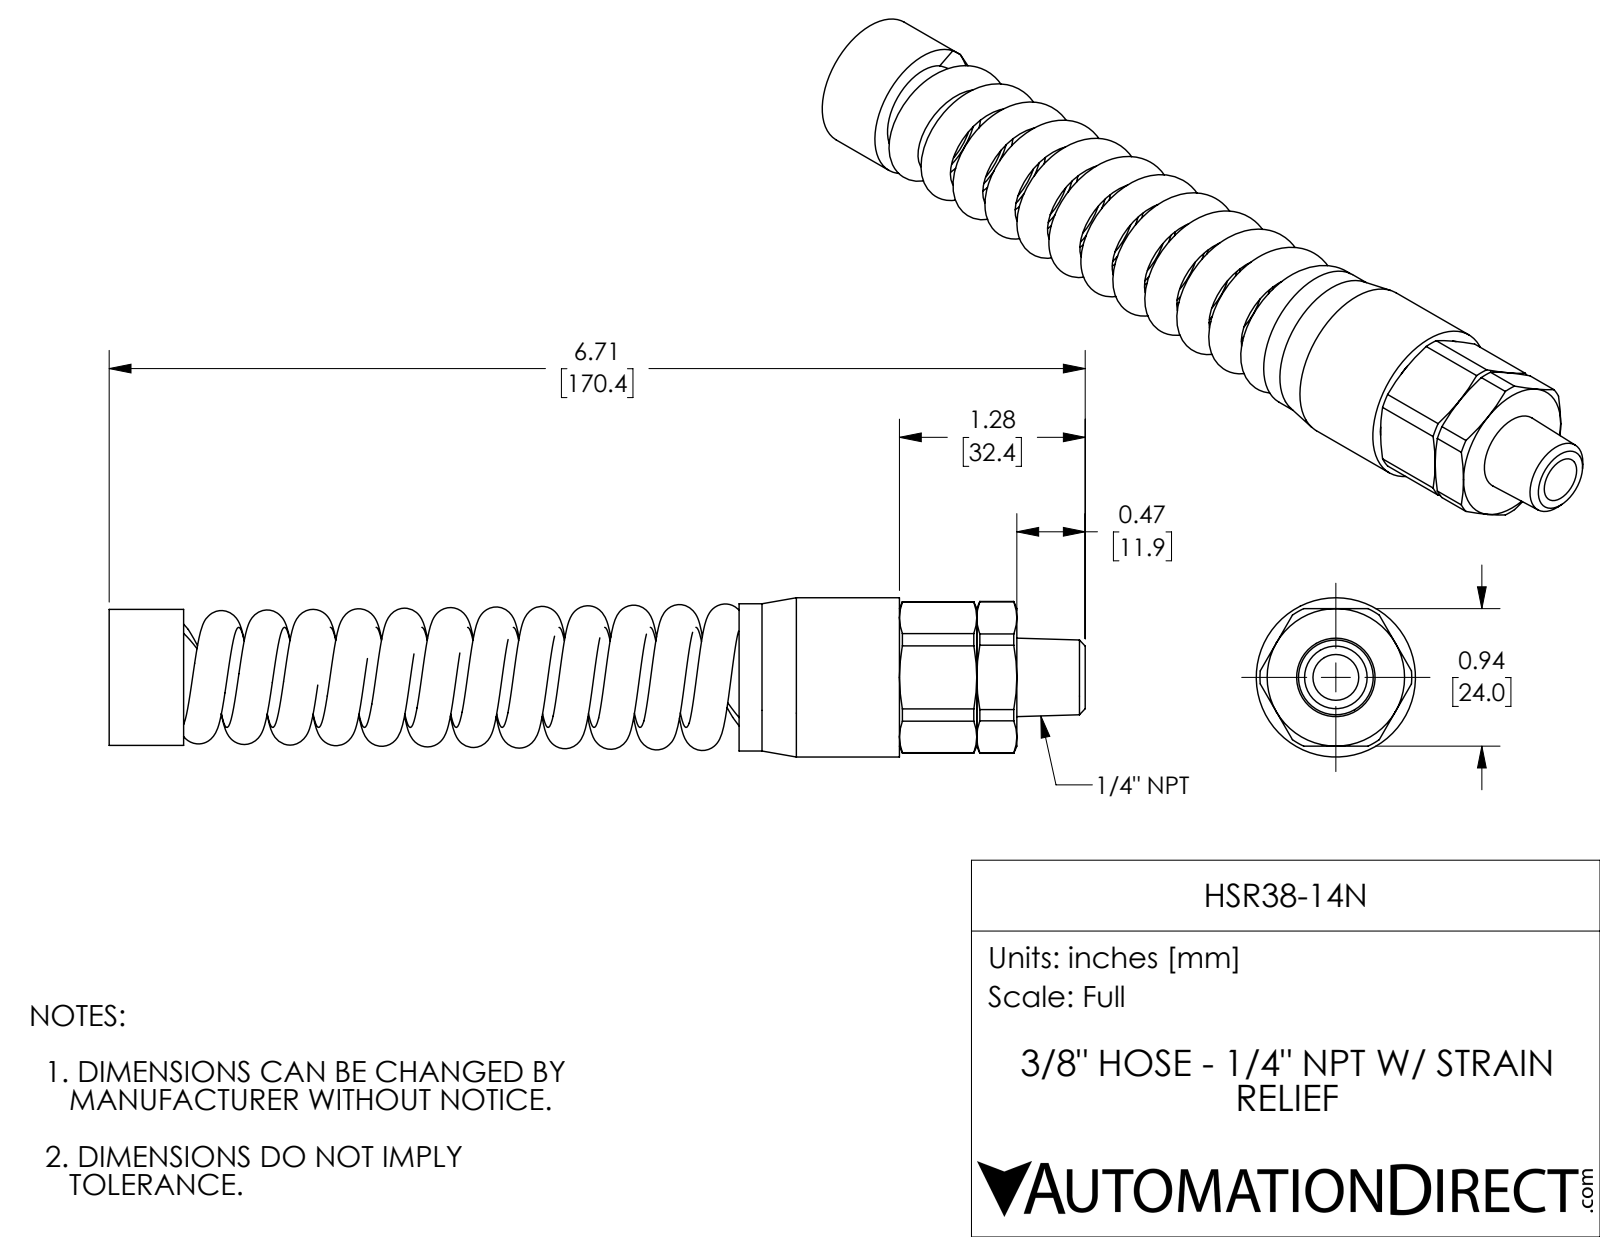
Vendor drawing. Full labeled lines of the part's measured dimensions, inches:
Part name (STEP PRODUCT): HSR38-14N
STEP written by: SolidWorks 2017 (AUTOMOTIVE_DESIGN)
Units: inches
Bodies: 3 solids, 136 faces (34 planar, 63 cylindrical, 39 other)
Overall size (bounding box): 6.71 × 1.094 × 1.094
Volume: 2.222 in³ · Surface area: 44.07 in²
Round holes (diameter × count): ⌀0.315 ×1, ⌀0.63 ×1, ⌀0.689 ×1, ⌀0.787 ×1, ⌀0.866 ×1, ⌀0.945 ×1
Round bosses / shafts (diameter × count): ⌀1.094 ×1, ⌀1.012 ×1, ⌀0.935 ×1, ⌀0.933 ×1, ⌀0.846 ×1, ⌀0.413 ×1
Partial cylindrical surfaces — rounded edges, fillets, slot ends (radius × count): R0.52 ×1, R0.522 ×1
Main face-to-face distances: 0.945, 0.276, 4.744, 0.512, 0.453, 0.728, 5.512, 5.965, 6.24, 4.331
